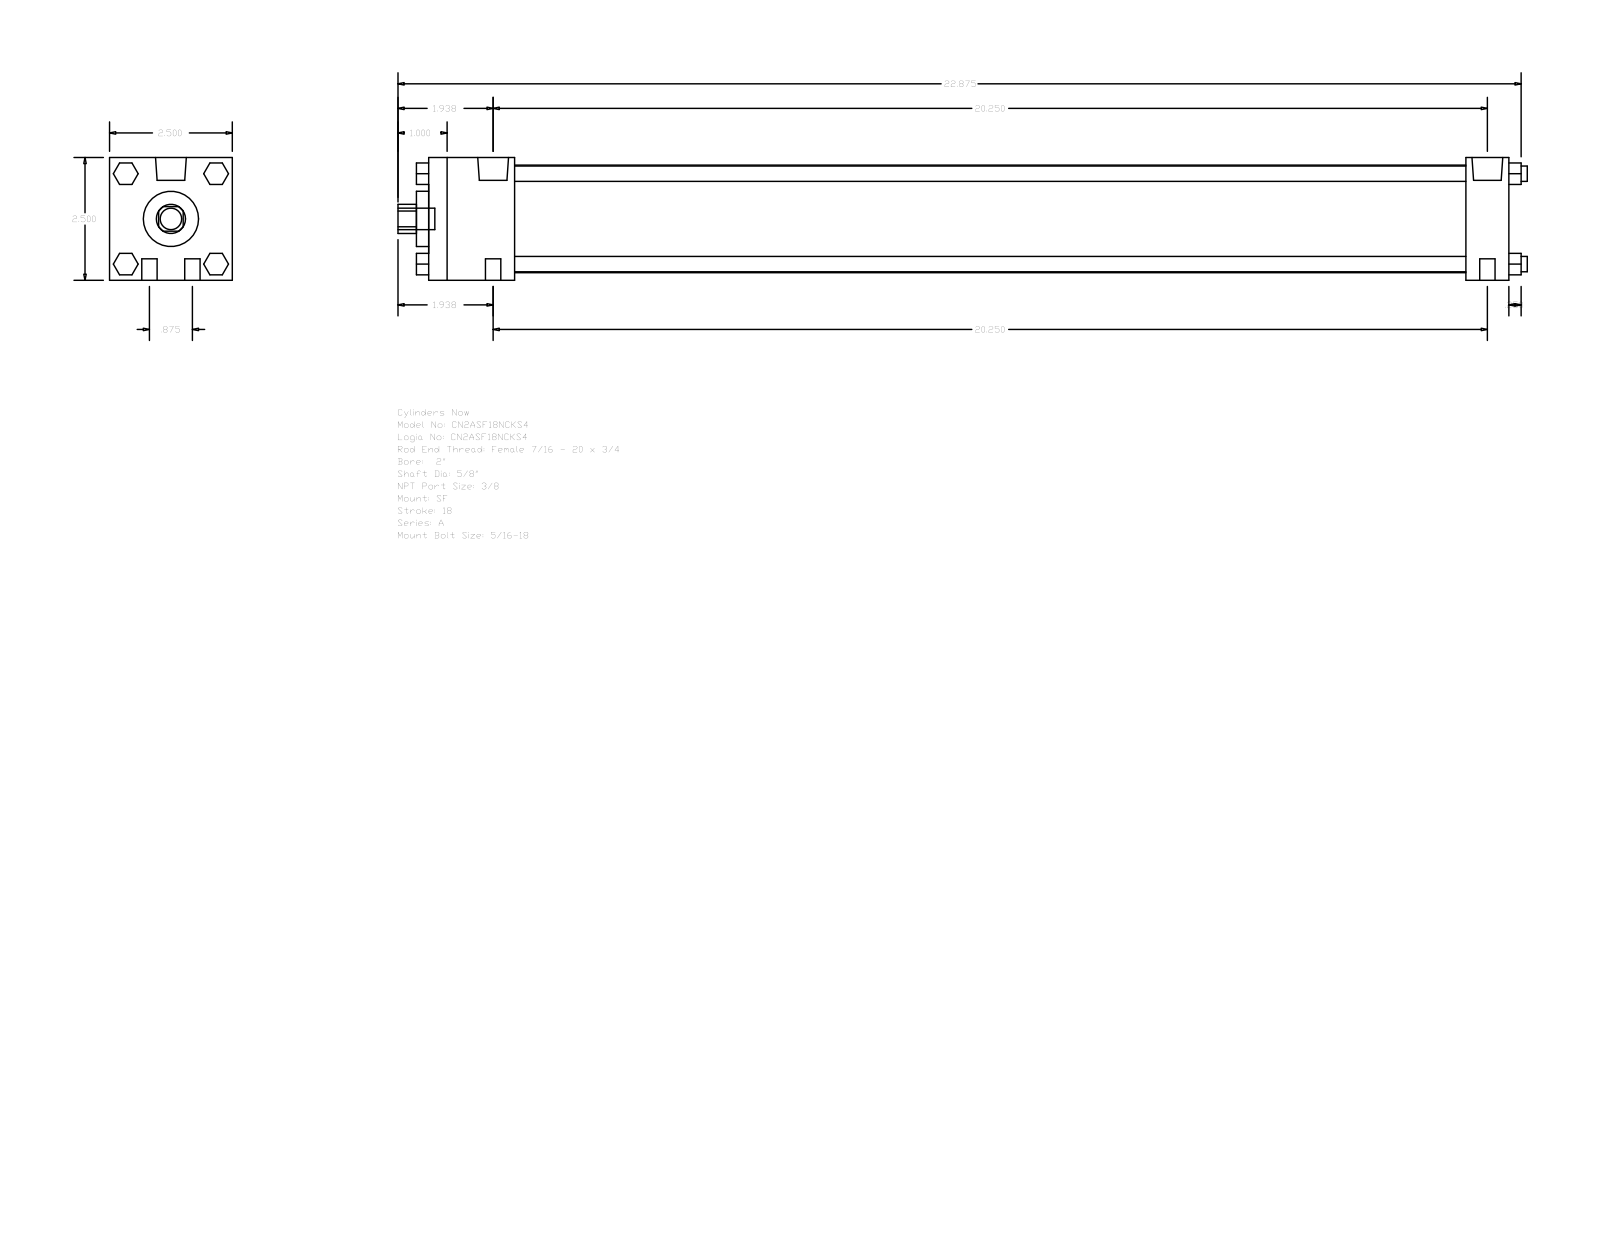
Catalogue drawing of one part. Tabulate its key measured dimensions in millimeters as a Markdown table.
| quantity | value |
| --- | --- |
| part name | A_SF__0200_0.625 |
| STEP written by | GSSL Pune (CONFIG_CONTROL_DESIGN) |
| units | millimeters |
| bodies | 0 solids, 124 faces (94 planar, 30 cylindrical, 0 other) |
| overall size | 584.2 × 63.5 × 63.5 |
| round holes (diameter × count) | 15.88 × 1, 28.57 × 1, 55.63 × 1 |
| round bosses / shafts (diameter × count) | 7.94 × 8, 15.93 × 2, 5.56 × 2, 11.11 × 1 |
| partial cylindrical surfaces (radius × count) | 7.54 × 1 |
| main face-to-face distances | 63.5, 558.79, 536.57, 22.22, 44.45, 492.12, 514.34, 6.35, 565.14, 50.8 |
